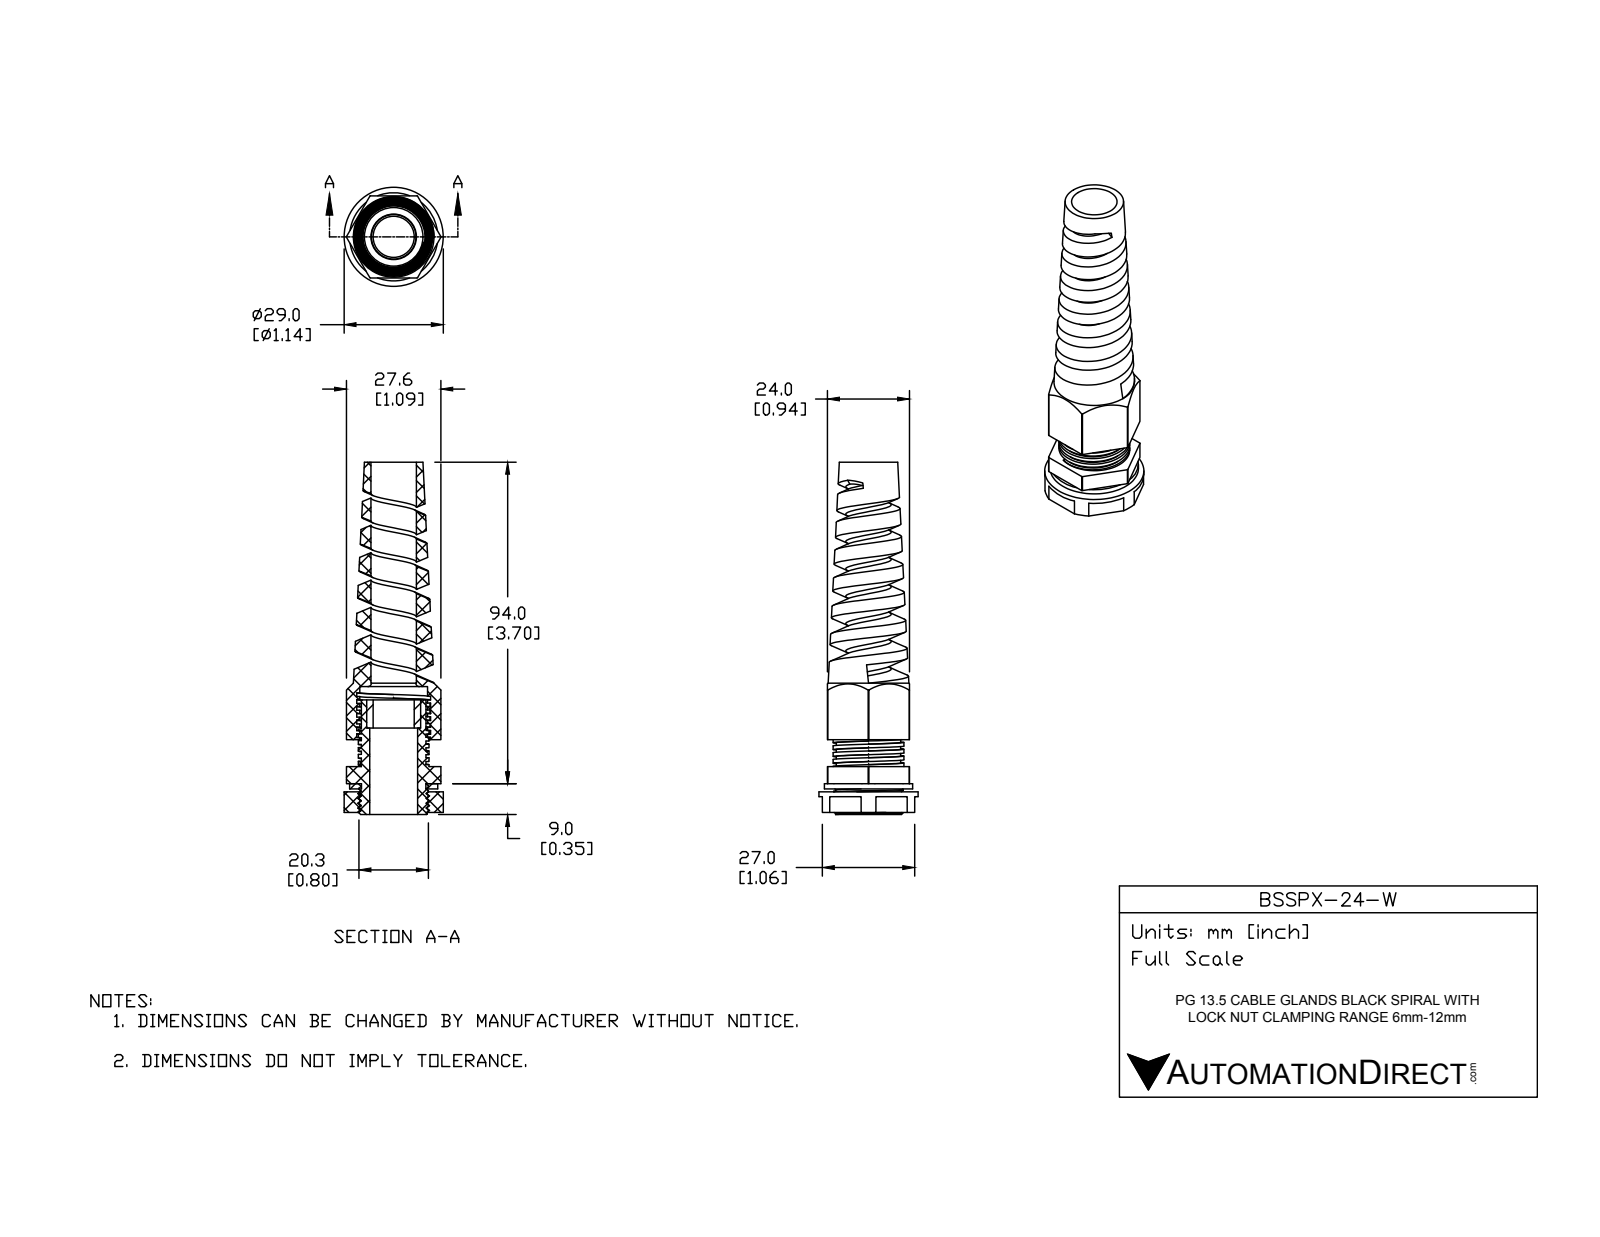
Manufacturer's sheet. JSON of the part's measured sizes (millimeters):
{"part_name": "BSSPX-24-W", "step_written_by": "SolidWorks 2015 (CONFIG_CONTROL_DESIGN)", "units": "millimeters", "bodies": {"solids": 5, "faces": 238, "planar": 105, "cylindrical": 97, "other": 36}, "overall_size": [103, 29, 29], "volume_mm3": 19417, "surface_area_mm2": 19983, "round_holes": [[12, 1], [13.3, 1], [14, 1], [15.8, 1], [18.8, 1], [19.63, 1], [19.79, 1]], "round_bosses_or_shafts": [[29, 1], [25.8, 1], [20.7, 1], [20.3, 1], [18.9, 1]], "partial_cylinders_radius": [[13.8, 1]], "face_to_face_distances": [24, 1.5, 2.5, 8.5, 6.5, 7.5, 27, 6, 25.5, 0.5]}
